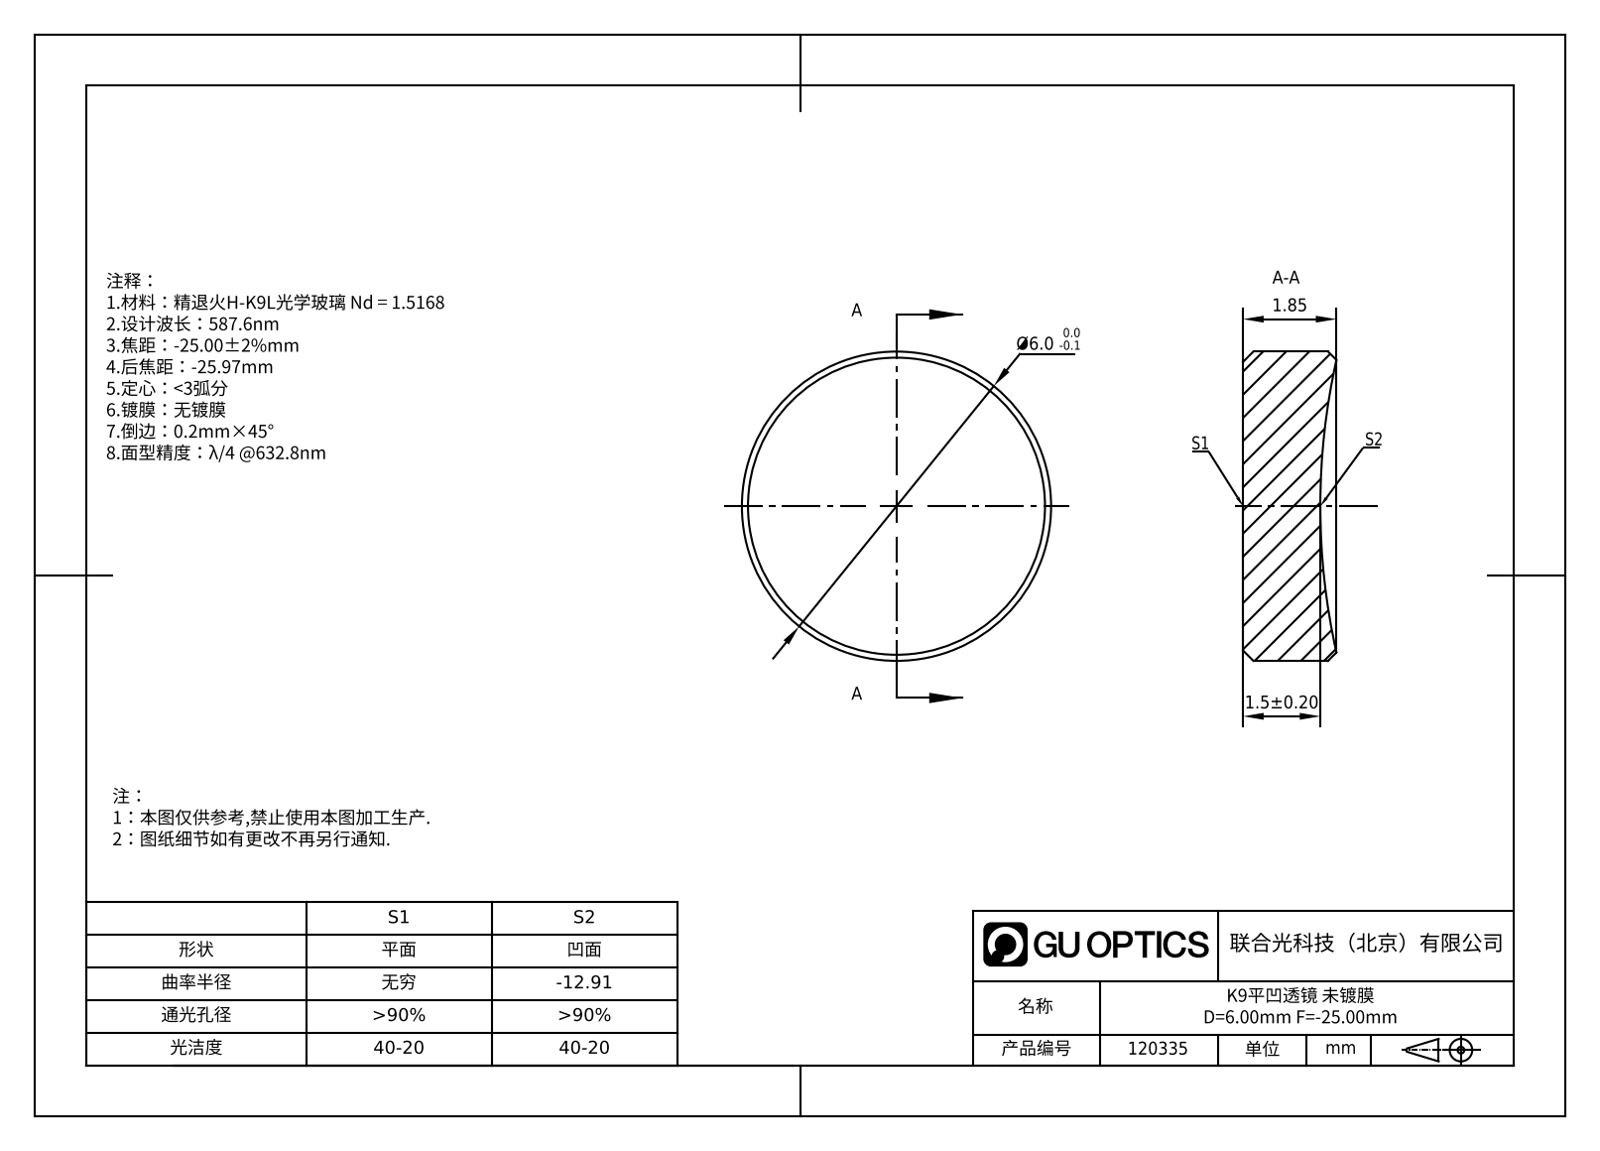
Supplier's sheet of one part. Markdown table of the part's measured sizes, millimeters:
| quantity | value |
| --- | --- |
| part name | GL13-006A-025 |
| STEP written by | SolidWorks 2022 (AUTOMOTIVE_DESIGN) |
| units | millimeters |
| bodies | 1 solid, 9 faces (1 planar, 2 cylindrical, 6 other) |
| overall size | 6 × 6 × 1.81 |
| volume | 47 mm³ |
| surface area | 87 mm² |
| round bosses / shafts (diameter × count) | 6 × 1 |
